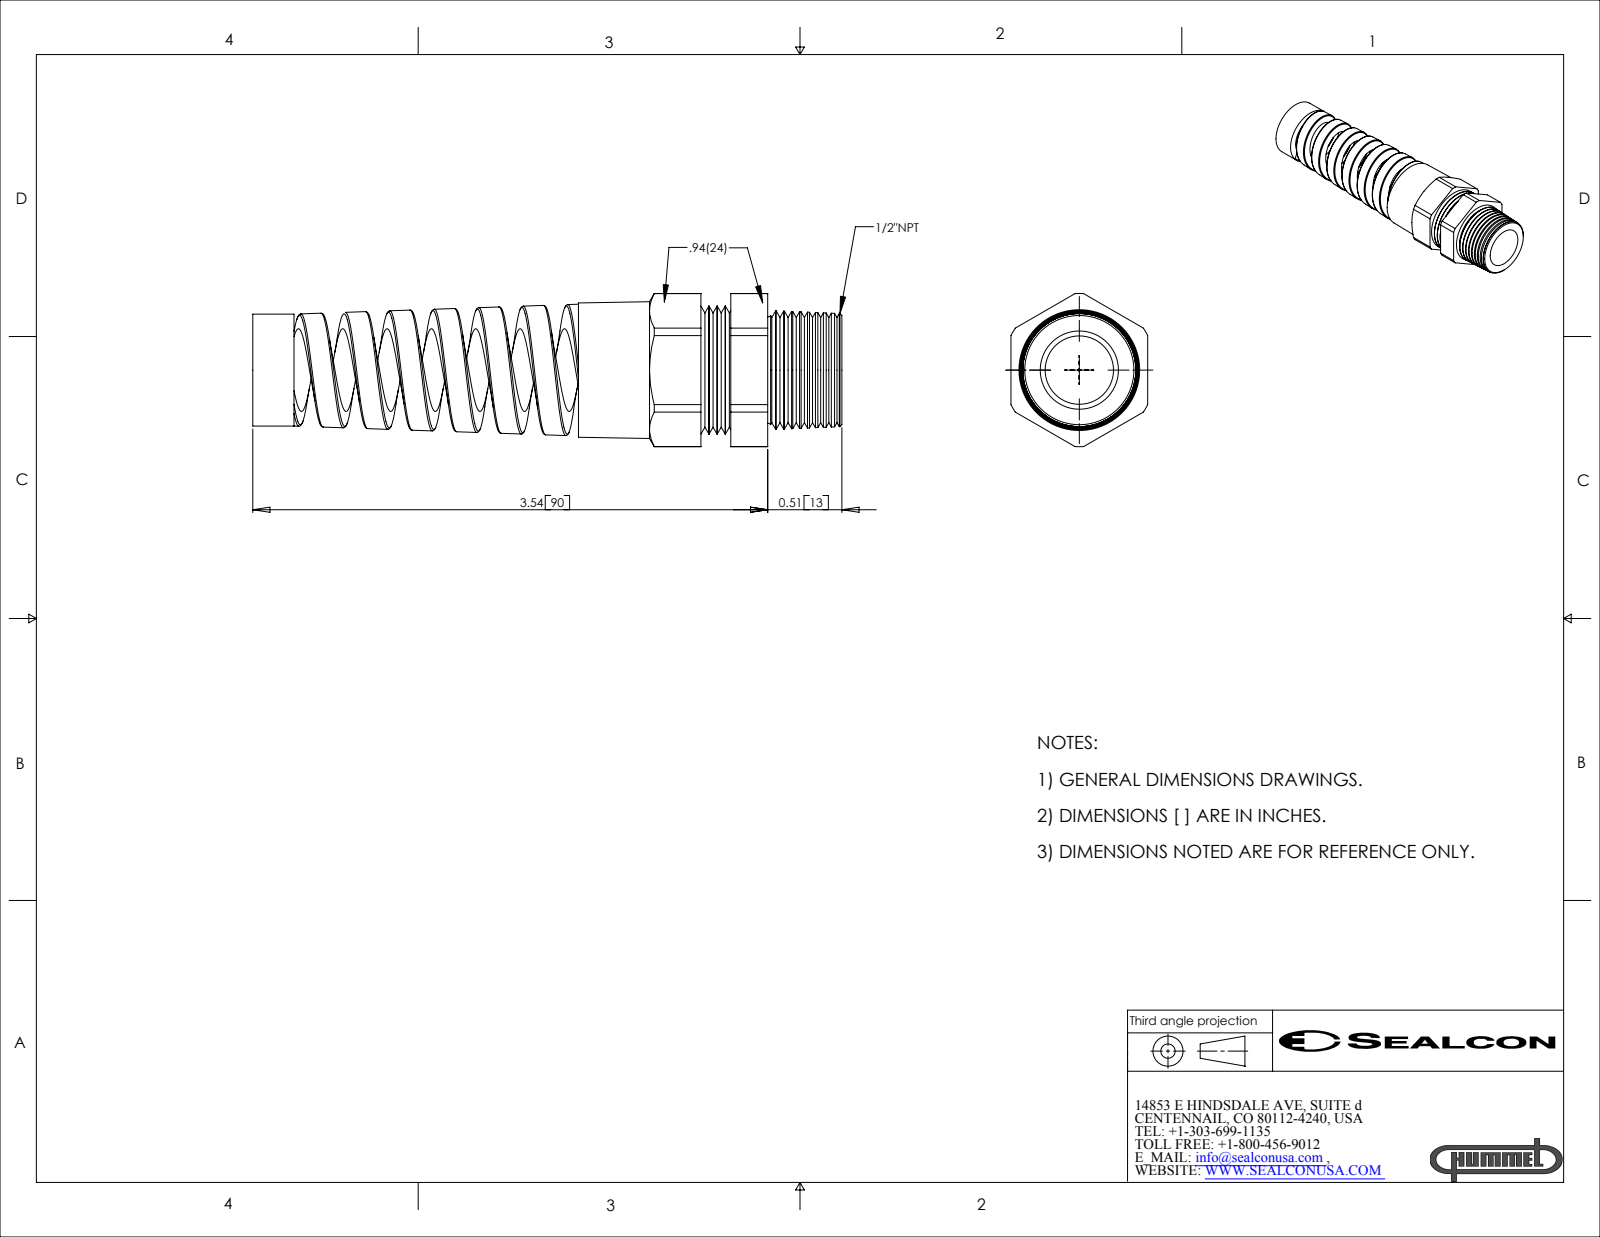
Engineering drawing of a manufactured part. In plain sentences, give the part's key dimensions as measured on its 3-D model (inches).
The part is named "CF13NA-BK". Its 3-D file was written by "SolidWorks 2007 (CONFIG_CONTROL_DESIGN)". It is 1 solid with 164 faces: 19 planar, 39 cylindrical and 106 other. Overall it measures 4.05 by 1.053 by 0.94 inches. Its volume is 1.176 cubic inches and its surface area 20.68 square inches. Round holes: 1 of diameter 0.47, 1 of diameter 0.569. Round bosses or shafts: 1 of diameter 0.88, 1 of diameter 0.769. Partial cylindrical surfaces (rounded edges, fillets, slot ends): 1 of radius 0.526. The main face-to-face distances are 0.94, 1.301, 1.811, 0.51, 2.239, 3.54, 4.05, 3.287, 1.048, 0.254.
